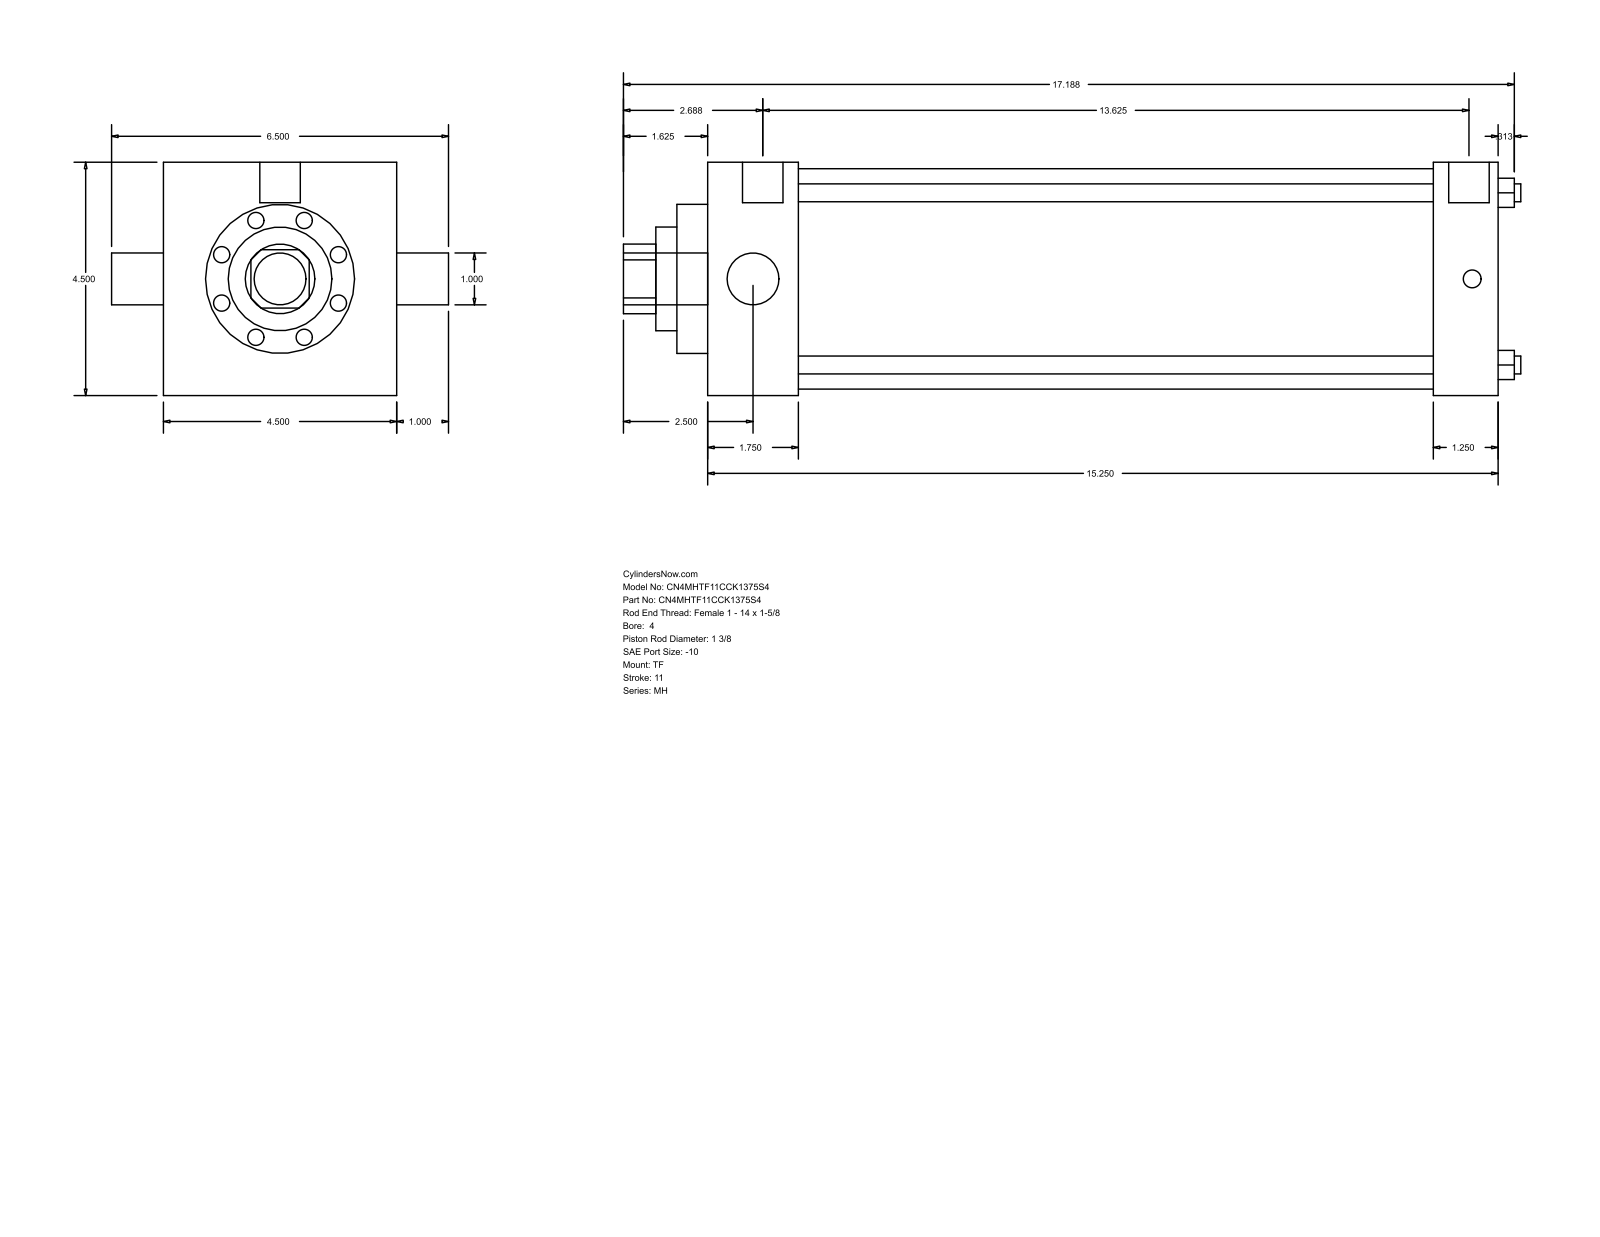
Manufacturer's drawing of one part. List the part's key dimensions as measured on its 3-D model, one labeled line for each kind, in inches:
Part name (STEP PRODUCT): MH_TF__0400_1.375
STEP written by: GSSL Pune (CONFIG_CONTROL_DESIGN)
Units: inches
Bodies: 0 solids, 86 faces (61 planar, 25 cylindrical, 0 other)
Overall size (bounding box): 17.313 × 6.5 × 4.5
Round holes (diameter × count): ⌀0.345 ×4, ⌀1 ×1, ⌀1.375 ×1, ⌀2 ×1, ⌀2.875 ×1, ⌀4.25 ×1
Round bosses / shafts (diameter × count): ⌀0.344 ×3, ⌀0.781 ×2, ⌀1 ×1
Partial cylindrical surfaces — rounded edges, fillets, slot ends (radius × count): R0.672 ×1
Main face-to-face distances: 4.5, 15.25, 1.75, 13.5, 14, 12.25, 1.25, 0.594, 2.344, 14.594
Hole centre spacings: 2.347, 3.32, 4.695
